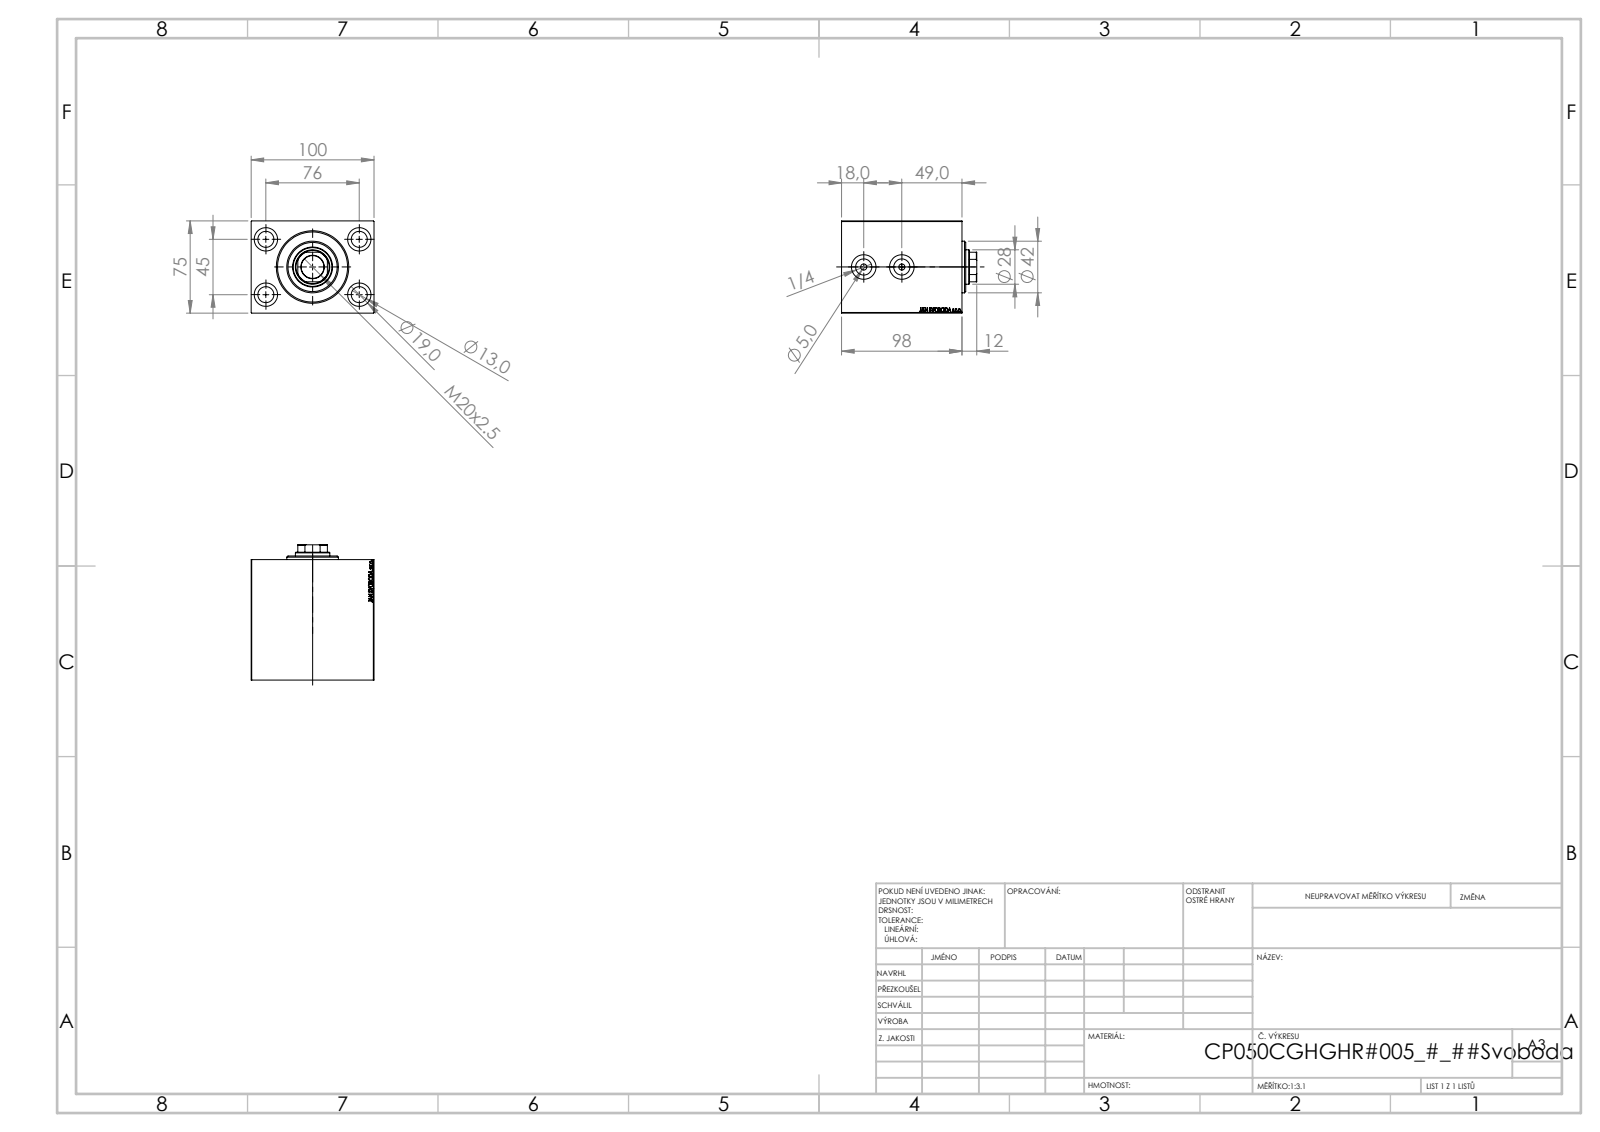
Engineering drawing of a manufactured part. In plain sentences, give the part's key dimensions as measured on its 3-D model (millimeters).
The part is named "V450CP_B_VCP; V450CP_VC_B; V450CP_C". Its 3-D file was written by "SolidWorks 2019 (CONFIG_CONTROL_DESIGN)". It is 3 solids with 888 faces: 414 planar, 76 cylindrical and 398 other. Overall it measures 110 by 100 by 75 millimeters. Its volume is 656 561 cubic millimeters and its surface area 114 396 square millimeters. Round holes: 4 of diameter 13, 4 of diameter 19, 2 of diameter 4, 2 of diameter 5, 2 of diameter 9.73, 2 of diameter 13.16, 2 of diameter 15, 2 of diameter 20, 1 of diameter 18.5, 1 of diameter 28, 1 of diameter 31.5, 1 of diameter 32.5. Round bosses or shafts: 1 of diameter 42. Partial cylindrical surfaces (rounded edges, fillets, slot ends): 1 of radius 13.5. The main face-to-face distances are 75, 100, 98, 49, 14, 84, 44, 5, 35, 13. The hole center spacings are 44.16, 45, 76, 88.32, 31, 42.55.
